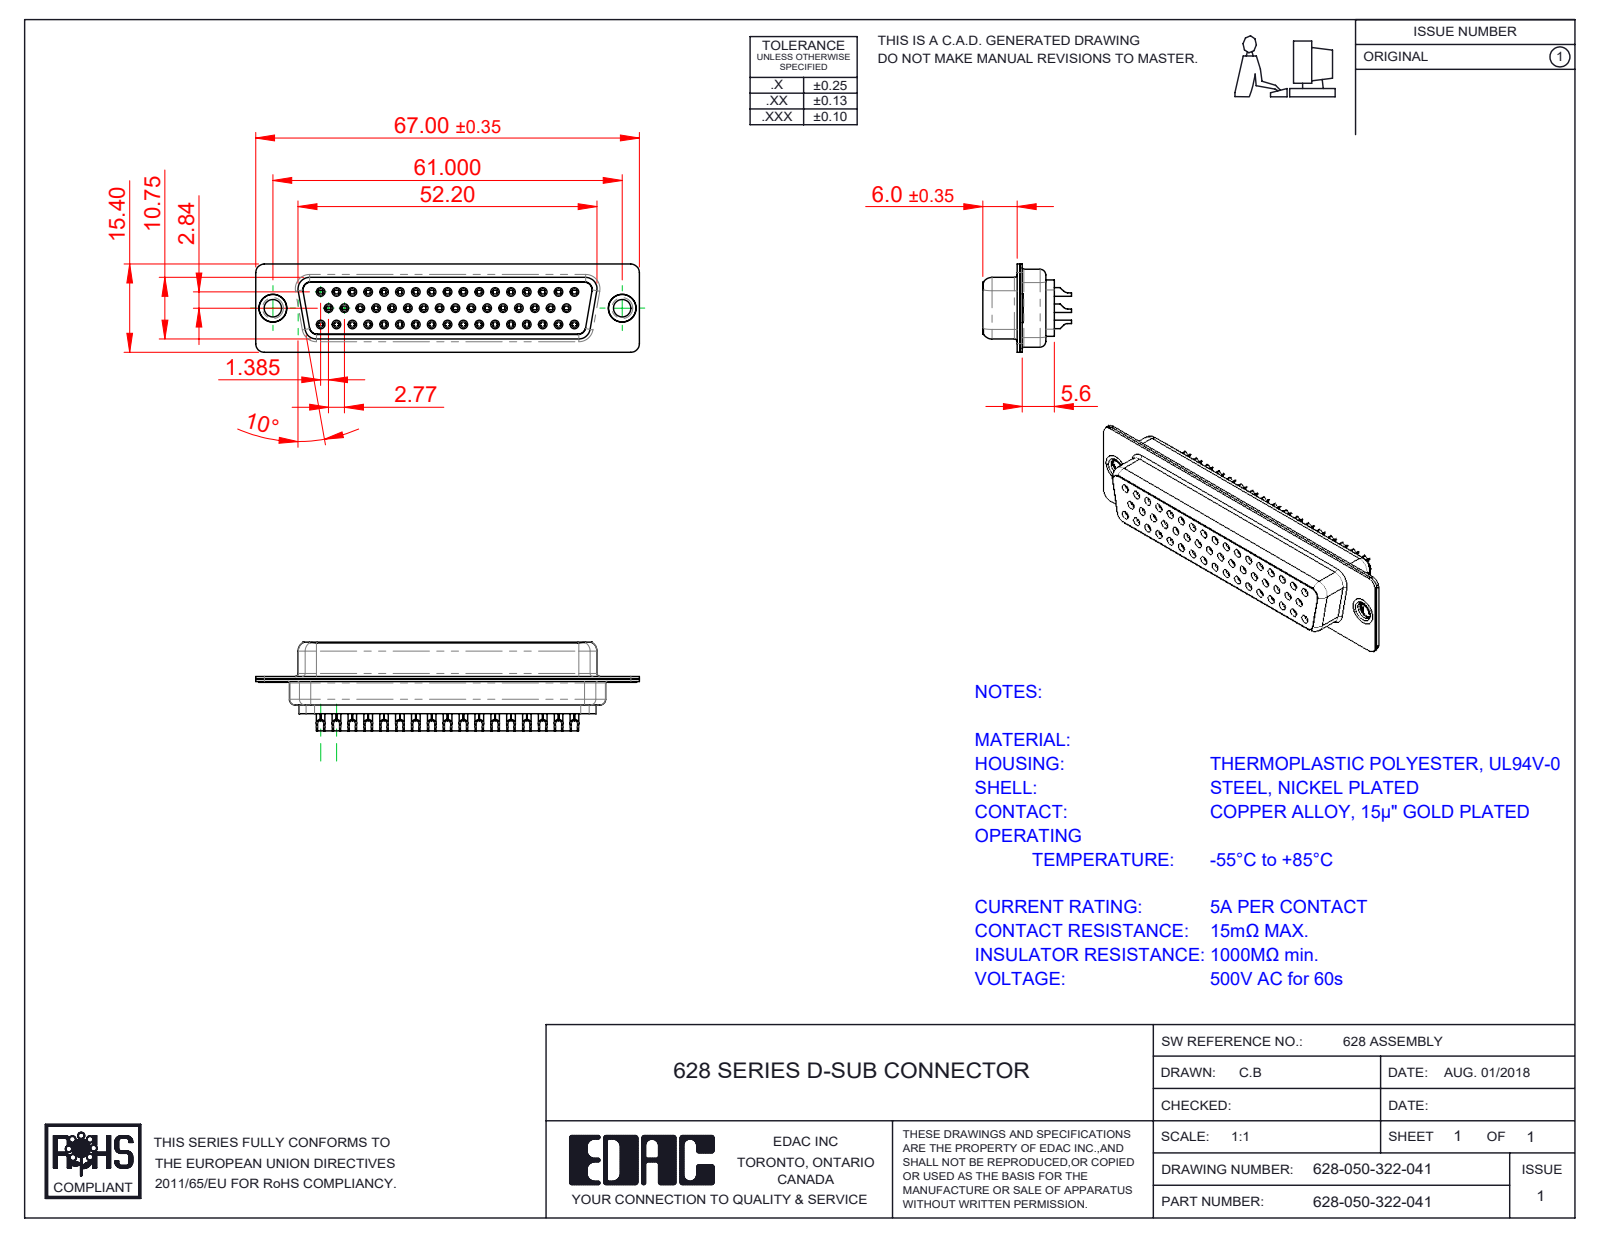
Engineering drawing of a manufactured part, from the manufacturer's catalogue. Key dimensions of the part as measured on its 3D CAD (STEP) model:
Part name (STEP PRODUCT): 628 Housing_50 LP; 628 Contact Row 1_22L; 628 Shell Front_50 Contacts; 628 Contact Row 2_22M (+4 more)
STEP written by: SolidWorks 2020 (CONFIG_CONTROL_DESIGN)
Units: millimetres
Bodies: 55 solids, 4703 faces (1117 planar, 1371 cylindrical, 2215 other)
Overall size (bounding box): 67 × 15.5 × 15.4
Volume: 6 691 mm³ · Surface area: 15 468 mm²
Round holes (diameter × count): ⌀0.8 ×50, ⌀0.9 ×50, ⌀1.1 ×50, ⌀1.6 ×50, ⌀1.7 ×17, ⌀3.05 ×2, ⌀4 ×2, ⌀4.05 ×2, ⌀4.85 ×2
Round bosses / shafts (diameter × count): ⌀2 ×50, ⌀1.5 ×50, ⌀1.2 ×50, ⌀5 ×2, ⌀4.95 ×2, ⌀4.8 ×2, ⌀3.55 ×2
Partial cylindrical surfaces — rounded edges, fillets, slot ends (radius × count): R0.28 ×33, R1.5 ×16, R2 ×12, R1.35 ×8, R1 ×7, R0.25 ×4, R0.5 ×4, R0.6 ×4
Main face-to-face distances: 0.45, 0.4, 11.33, 1.87, 0.9, 6.05, 6.5, 10.3, 12.5, 6.45
Hole centre spacings: 3.16, 2.77, 5.54, 8.31, 11.08, 13.85, 16.62, 19.39
